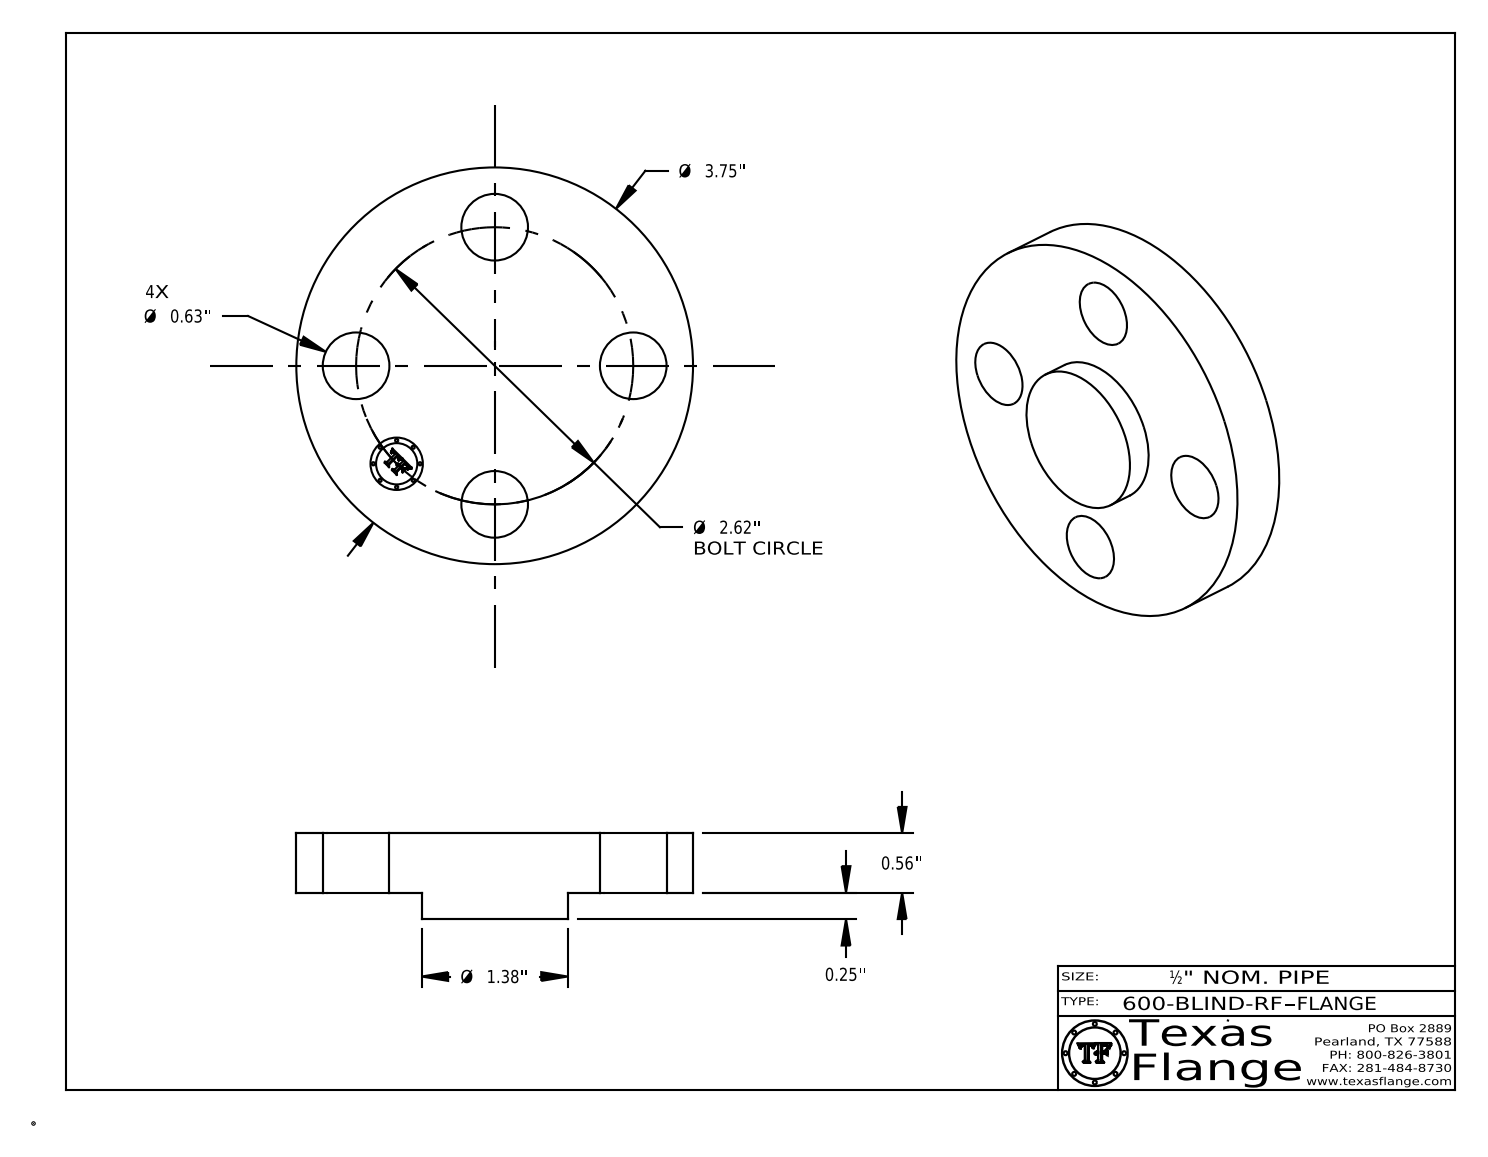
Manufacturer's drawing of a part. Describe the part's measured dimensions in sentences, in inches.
The part is named "600-BLIND-RF". Its 3-D file was written by "CATIA V5 STEP AP214 (AUTOMOTIVE_DESIGN)". It is 1 solid with 400 faces: 368 planar, 32 cylindrical and 0 other. Overall it measures 3.75 by 3.75 by 0.81 inches. Its volume is 5.859 cubic inches and its surface area 31.8 square inches. Round holes: 4 of diameter 0.63, 1 of diameter 0.495. Round bosses or shafts: 8 of diameter 0.03, 1 of diameter 3.75, 1 of diameter 1.38, 1 of diameter 0.39. The main face-to-face distances are 0.56, 0.25, 0.81, 0.795, 0.545, 0.015, 0.148, 0.144, 0.027, 0.096. The hole center spacings are 1.852, 1.003, 2.42, 2.62.
